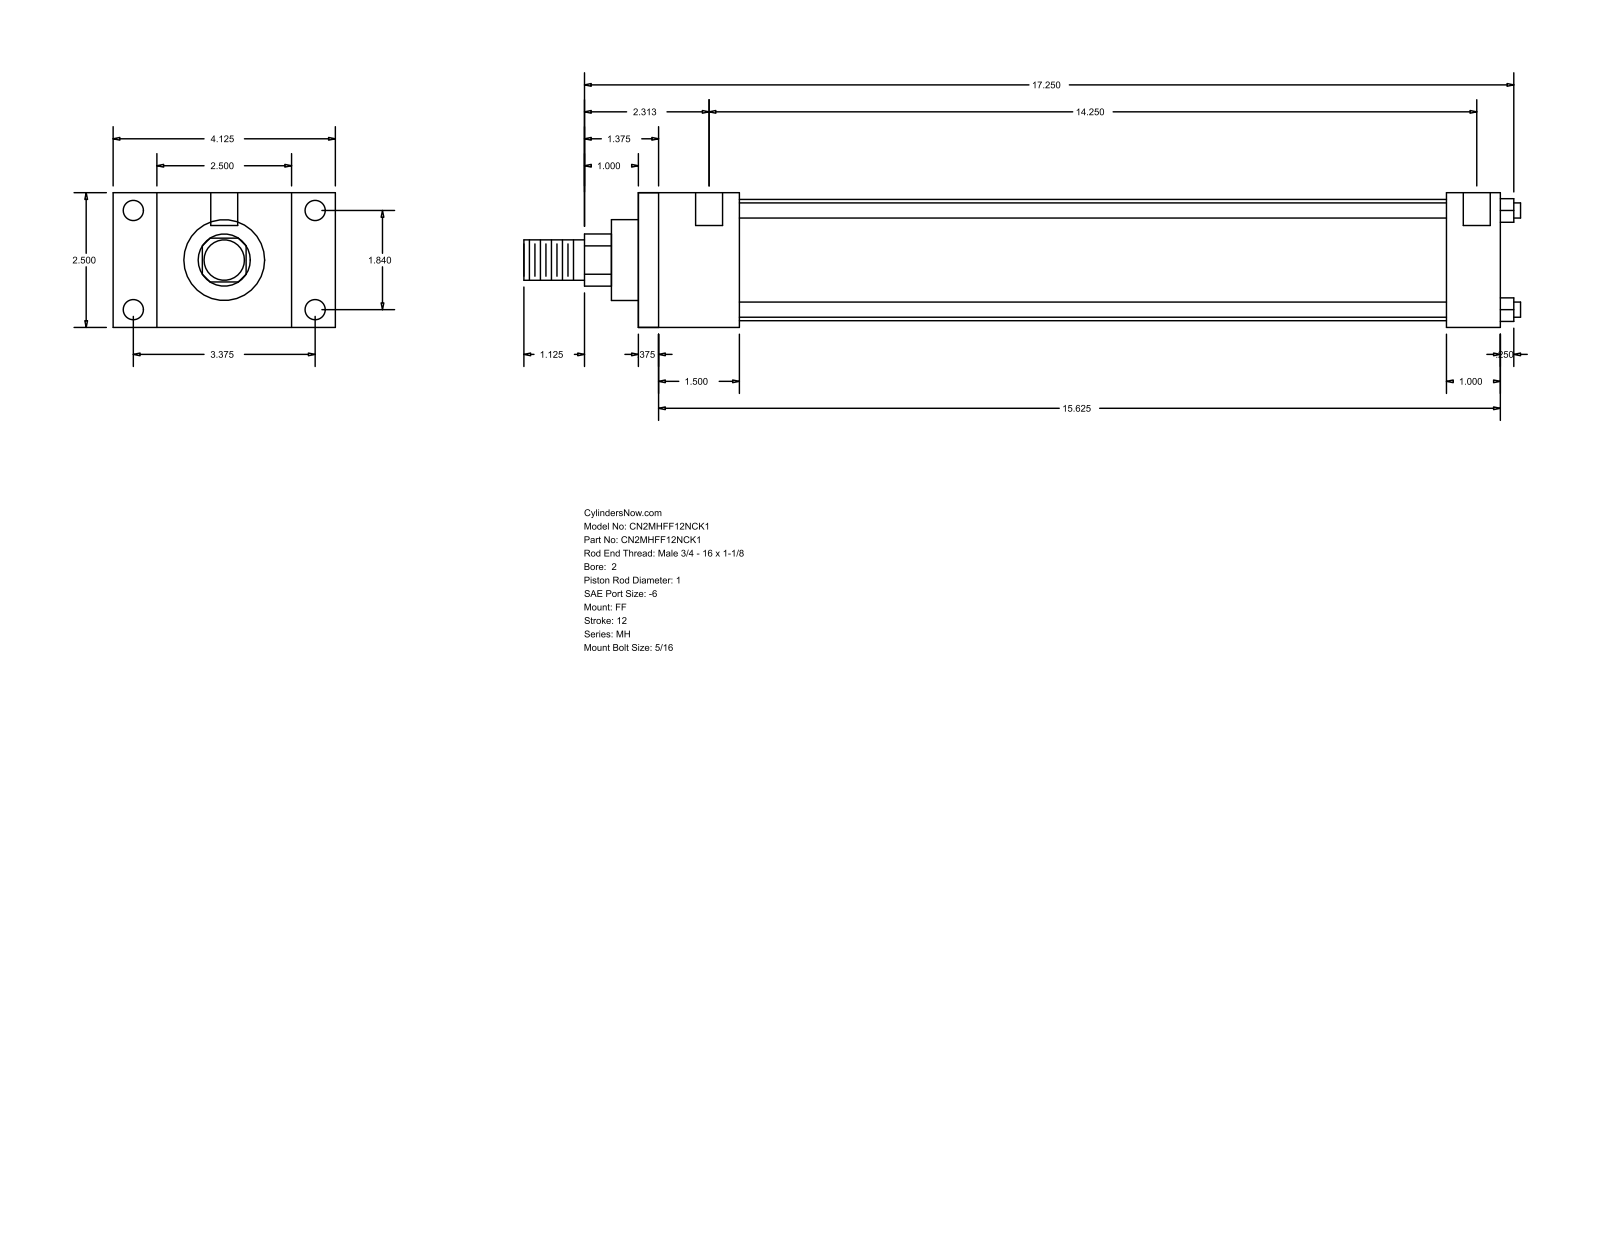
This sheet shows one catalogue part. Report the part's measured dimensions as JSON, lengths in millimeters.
{"part_name": "MH_FF__0200_1", "step_written_by": "GSSL Pune (CONFIG_CONTROL_DESIGN)", "units": "millimeters", "bodies": {"solids": 0, "faces": 92, "planar": 64, "cylindrical": 28, "other": 0}, "overall_size": [469.9, 104.78, 63.5], "round_holes": [[5.56, 4], [9.53, 4], [12.7, 2]], "round_bosses_or_shafts": [[7.14, 4], [57.15, 1], [38.1, 1], [25.4, 1], [19.05, 1]], "partial_cylinders_radius": [[12.29, 1]], "face_to_face_distances": [63.5, 406.4, 9.52, 396.88, 20.64, 25.4, 47.63, 381, 38.11, 371.48], "hole_center_spacings": [46.74, 85.72, 97.63, 369.88, 3.17, 4.76, 361.95, 365.12]}
